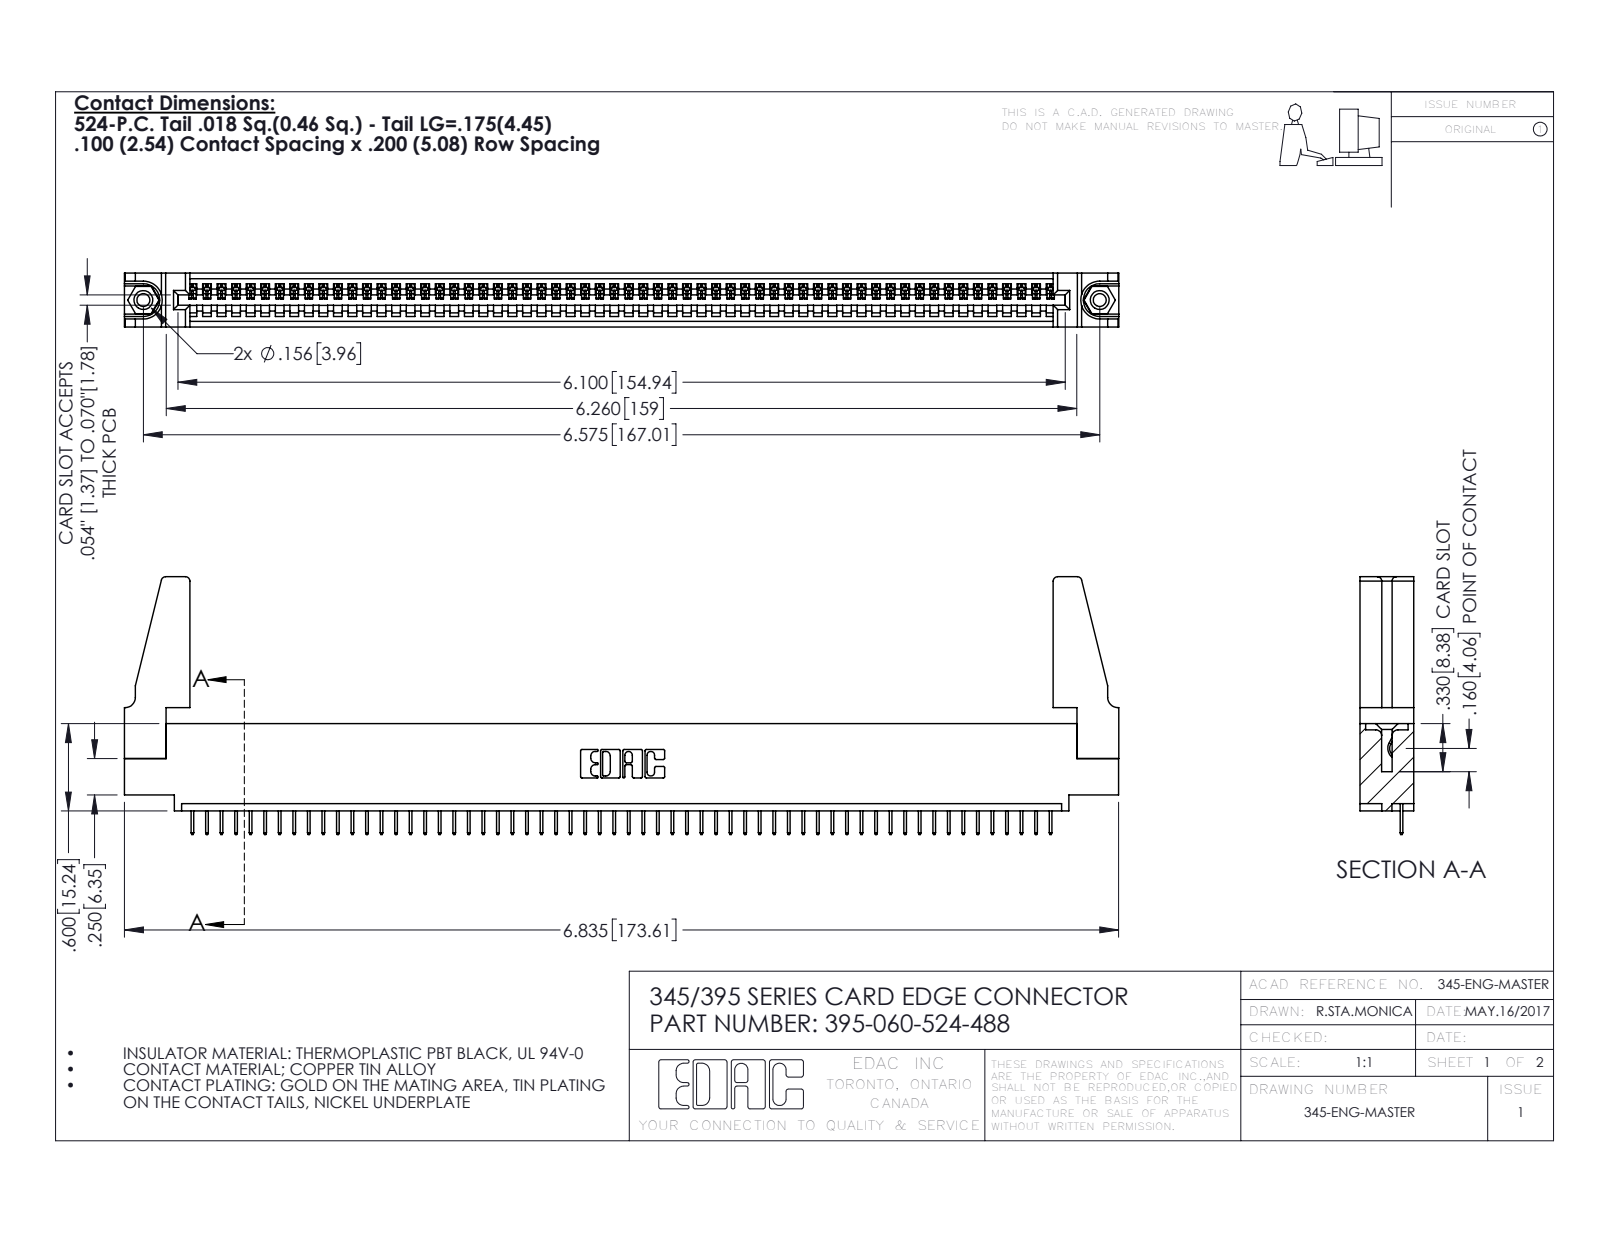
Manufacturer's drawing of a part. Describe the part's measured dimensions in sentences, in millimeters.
The part is named "395-060-524-488; 345-220-078_345-220-088; 345-250-001_345-250-001-102; 345-292-001_345-293-124 (+1 more)". Its 3-D file was written by "SolidWorks 2016 (CONFIG_CONTROL_DESIGN)". It is 65 solids with 3974 faces: 2916 planar, 1042 cylindrical and 16 other. Overall it measures 173.6 by 45 by 9.4 millimeters. Its volume is 19 580 cubic millimeters and its surface area 24 400 square millimeters. Round holes: 2 of diameter 2.3, 2 of diameter 3.2, 2 of diameter 4, 1 of diameter 1.6. Round bosses or shafts: 2 of diameter 3.9. Partial cylindrical surfaces (rounded edges, fillets, slot ends): 120 of radius 0.2, 22 of radius 0.3, 8 of radius 0.8, 6 of radius 0.2, 6 of radius 0.8, 3 of radius 0.7, 2 of radius 0.8, 2 of radius 1. The main face-to-face distances are 1.8, 7.6, 9.4, 5.1, 2.5, 6.9, 0.6, 5.7, 1.8, 3.8. The hole center spacings are 6.9, 161, 167.
